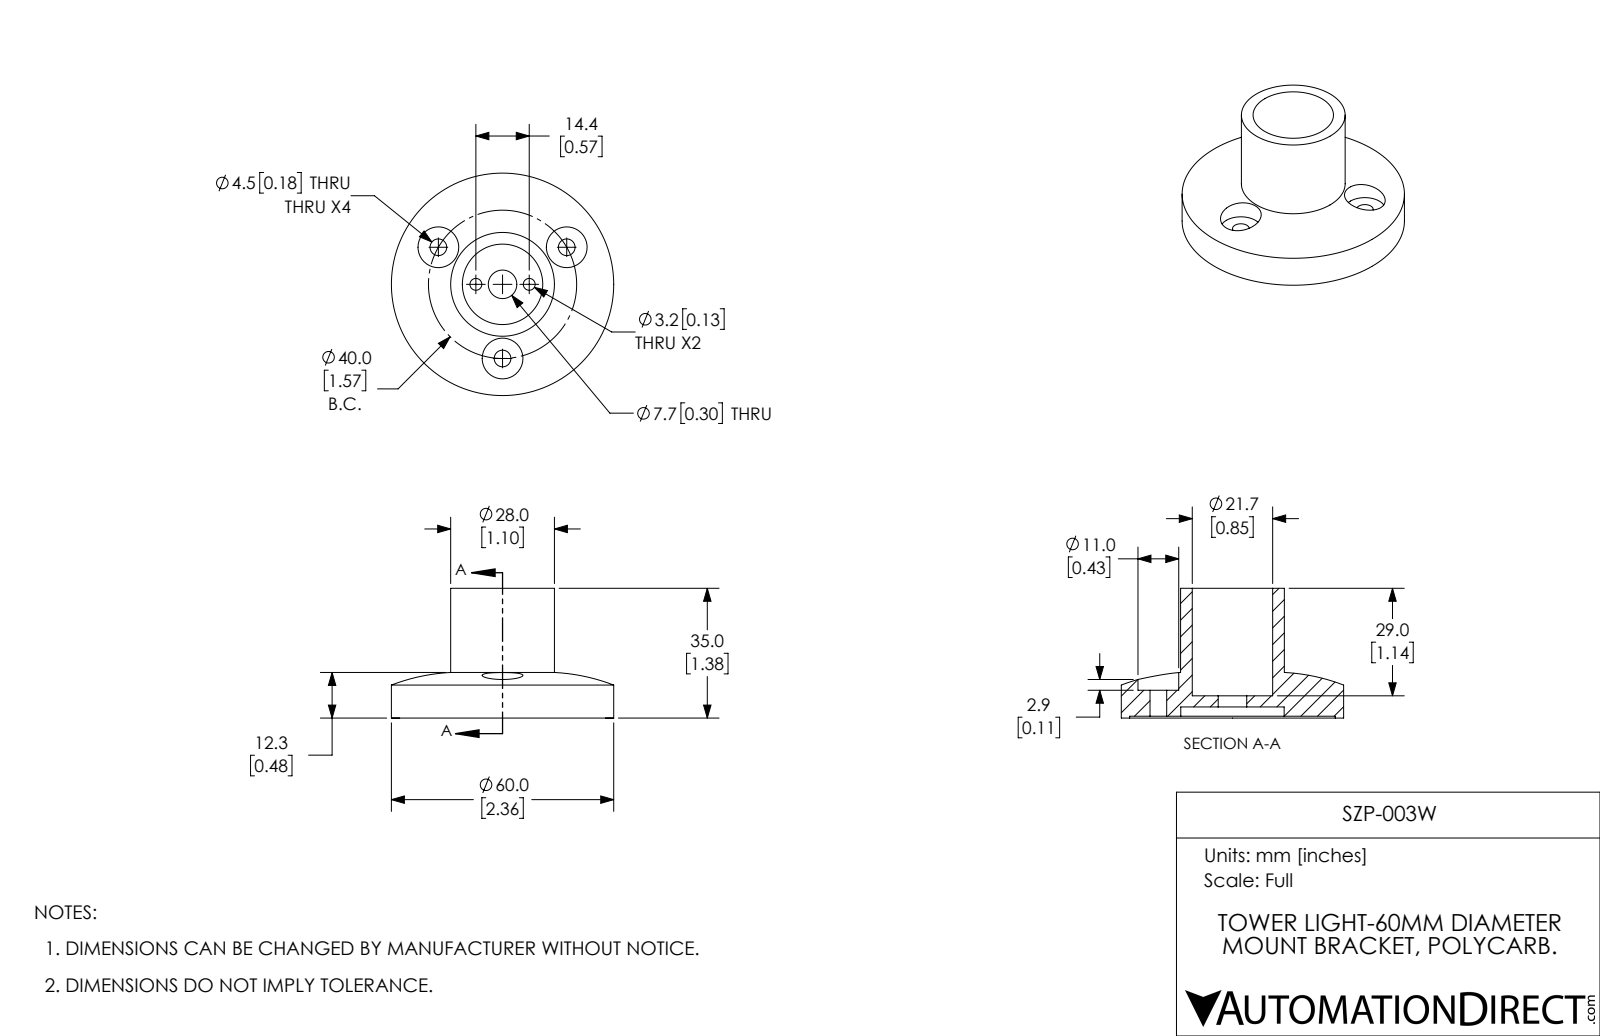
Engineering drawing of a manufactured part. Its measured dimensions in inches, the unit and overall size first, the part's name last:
Units: inches
Overall size (bounding box): 2.362 × 2.362 × 1.378
Round holes (diameter × count): ⌀0.177 ×3, ⌀0.433 ×3, ⌀0.126 ×2, ⌀0.303 ×1, ⌀0.854 ×1, ⌀1.098 ×1, ⌀2.185 ×1
Round bosses / shafts (diameter × count): ⌀2.362 ×1, ⌀1.102 ×1
Main face-to-face distances: 0.098, 0.217, 0.118, 1.358, 1.26, 1.142, 0.276, 0.177, 0.059, 1.083
Hole centre spacings: 0.787, 1.364, 0.283, 0.56, 0.837, 1.043, 0.567
Volume: 1.855 in³ · Surface area: 19.05 in²
Bodies: 1 solid, 39 faces (7 planar, 28 cylindrical, 4 other)
Part name (STEP PRODUCT): SZP-003W
STEP written by: SolidWorks 2017 (AUTOMOTIVE_DESIGN)
